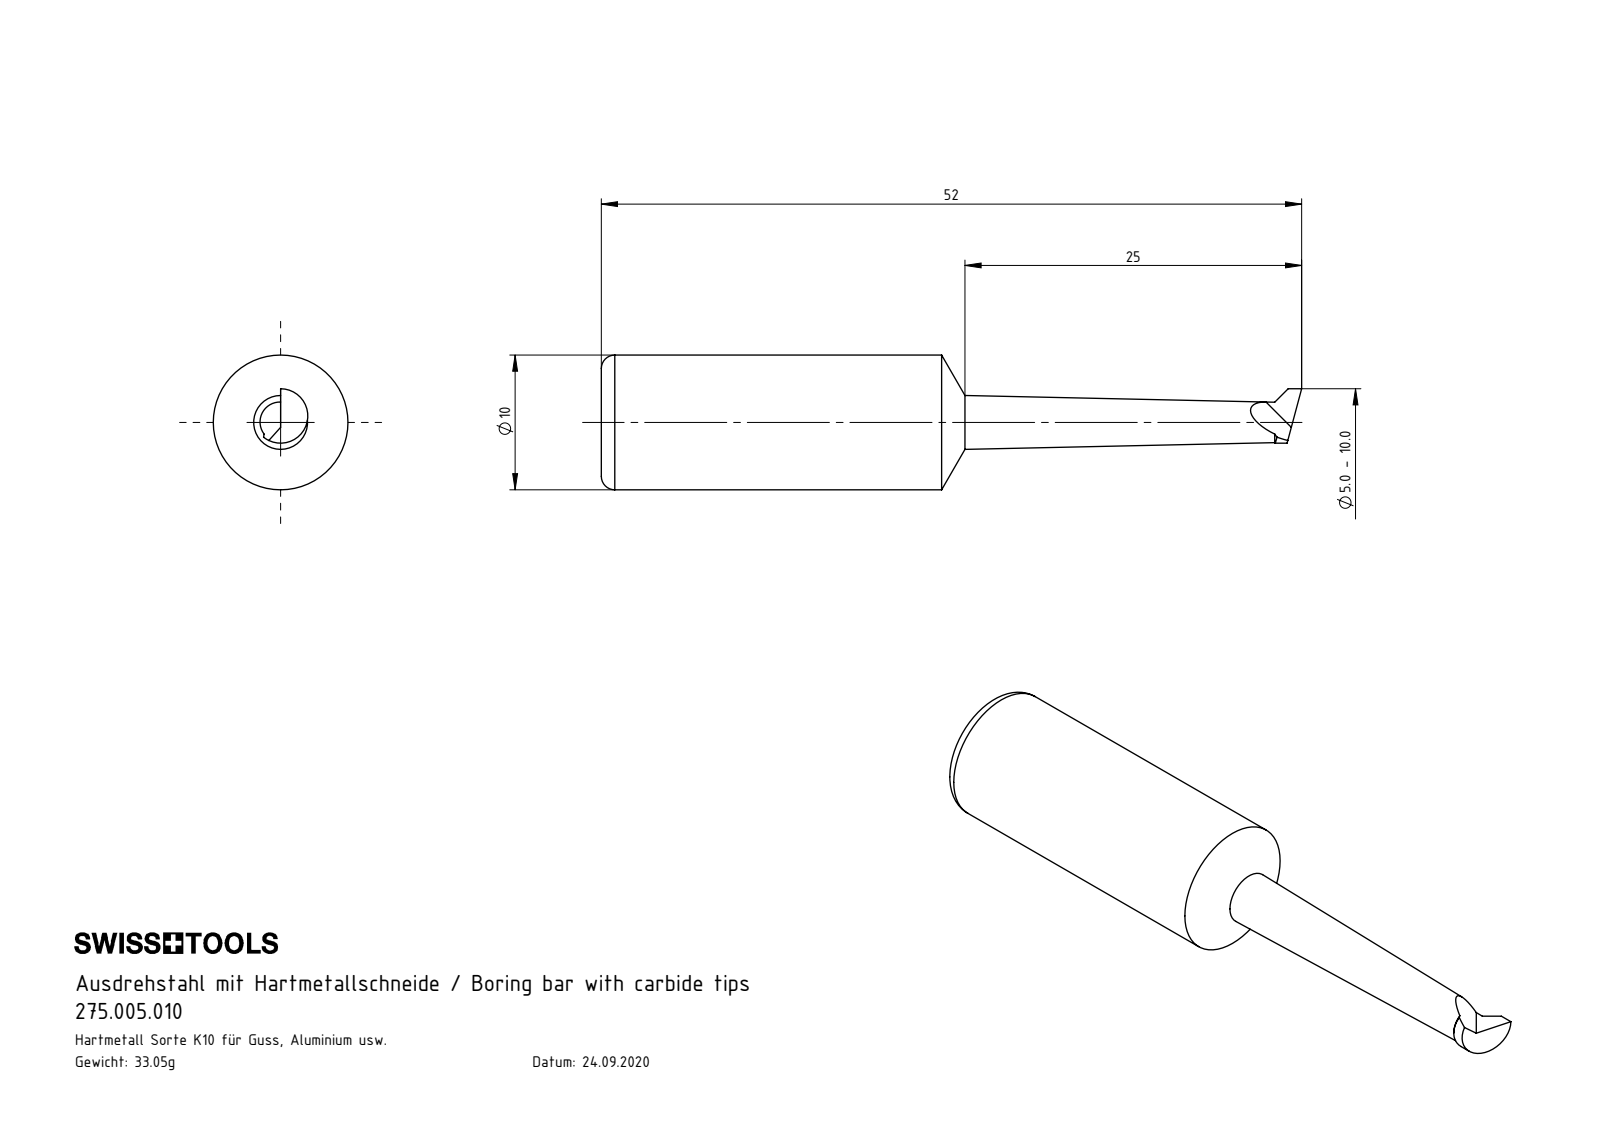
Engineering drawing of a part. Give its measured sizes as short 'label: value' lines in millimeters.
name: U10.B05.001.025
written by: SolidWorks 2012 (CONFIG_CONTROL_DESIGN)
unit: mm
bodies: 1 solid, 29 faces (3 planar, 3 cylindrical, 23 other)
size: 52 × 10 × 10
volume: 2 289 mm³; area: 1 222 mm²
bosses: 1× ⌀10
rounds: 1× R0.8
